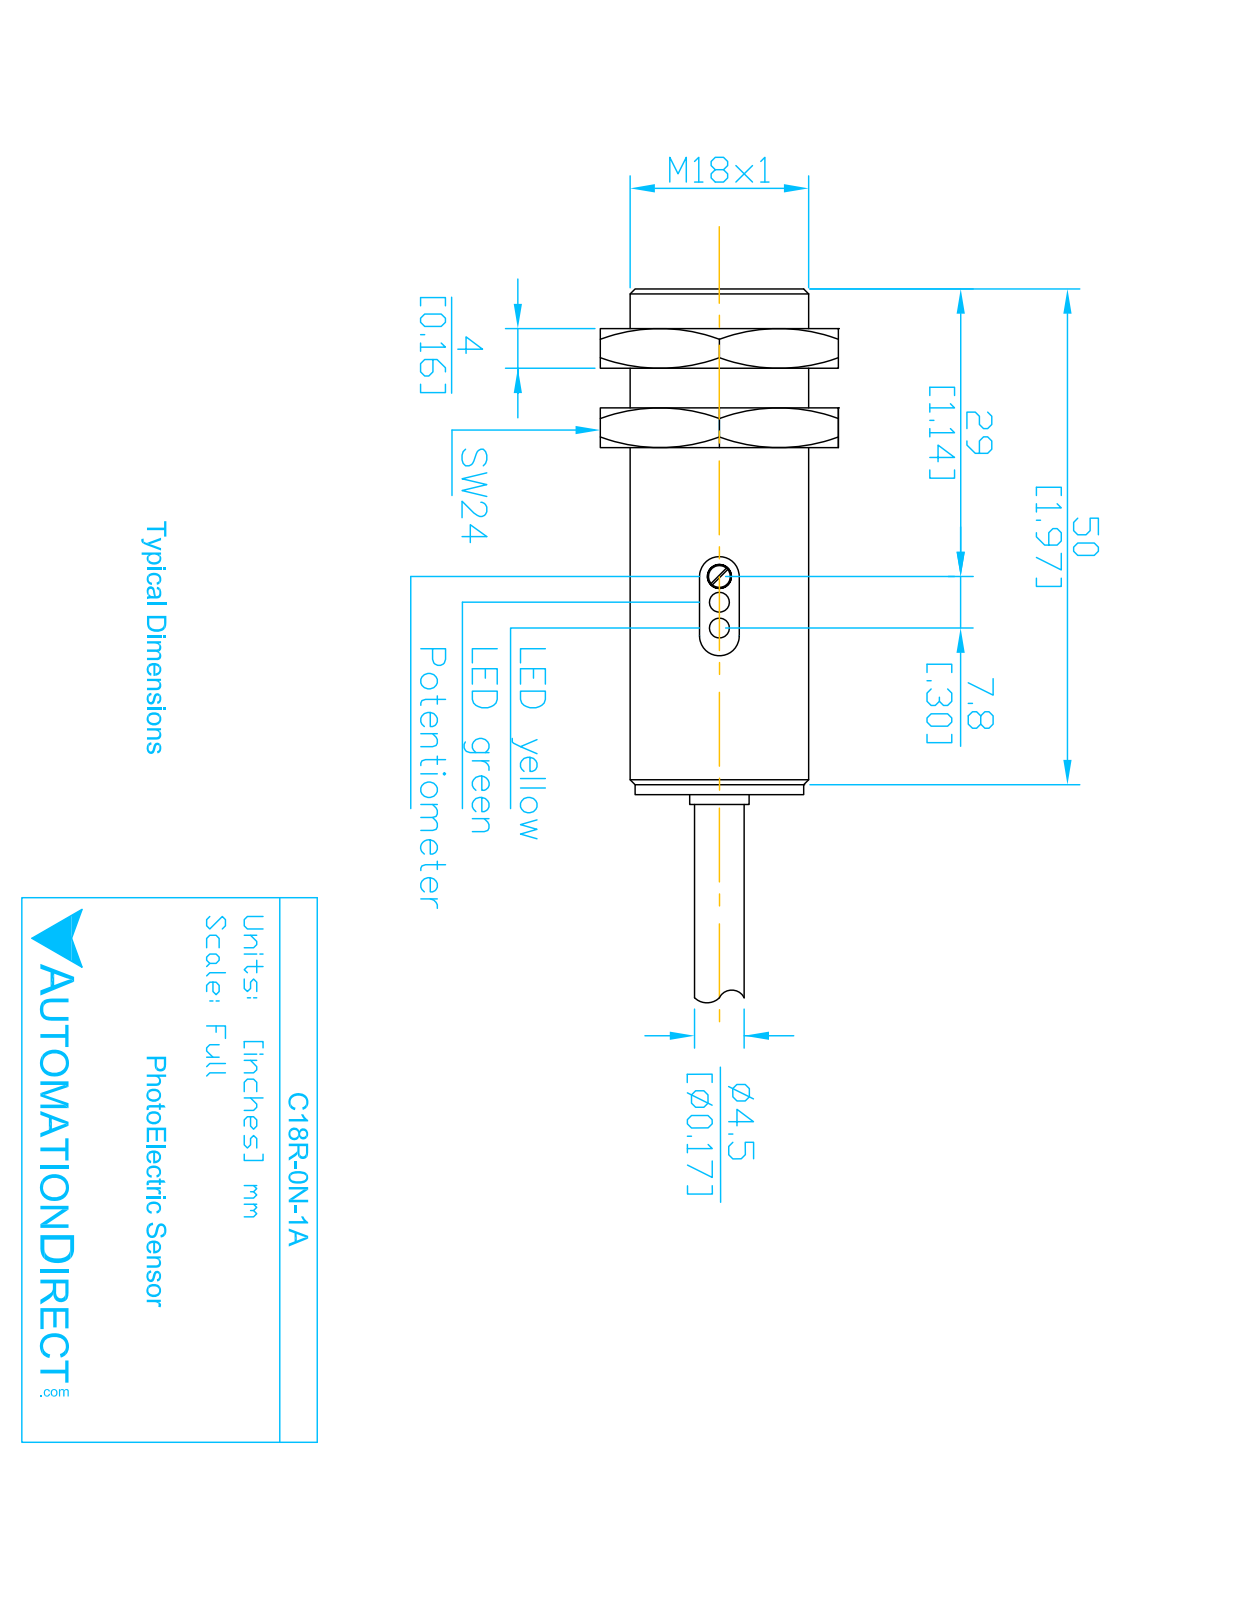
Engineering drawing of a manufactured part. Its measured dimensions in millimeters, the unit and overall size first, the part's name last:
Units: millimetres
Overall size (bounding box): 112.8 × 18 × 18
Round bosses / shafts (diameter × count): ⌀18 ×1, ⌀16.4 ×1, ⌀10.5 ×1, ⌀6.8 ×1, ⌀5 ×1
Main face-to-face distances: 51, 50.8, 51.8, 51.6, 0.8, 53, 52.8, 2, 1.2, 48
Volume: 17 010 mm³ · Surface area: 5 357 mm²
Bodies: 3 solids, 30 faces (12 planar, 5 cylindrical, 13 other)
Part name (STEP PRODUCT): C18E-00-1A
STEP written by: SolidWorks 2017 (AUTOMOTIVE_DESIGN)
